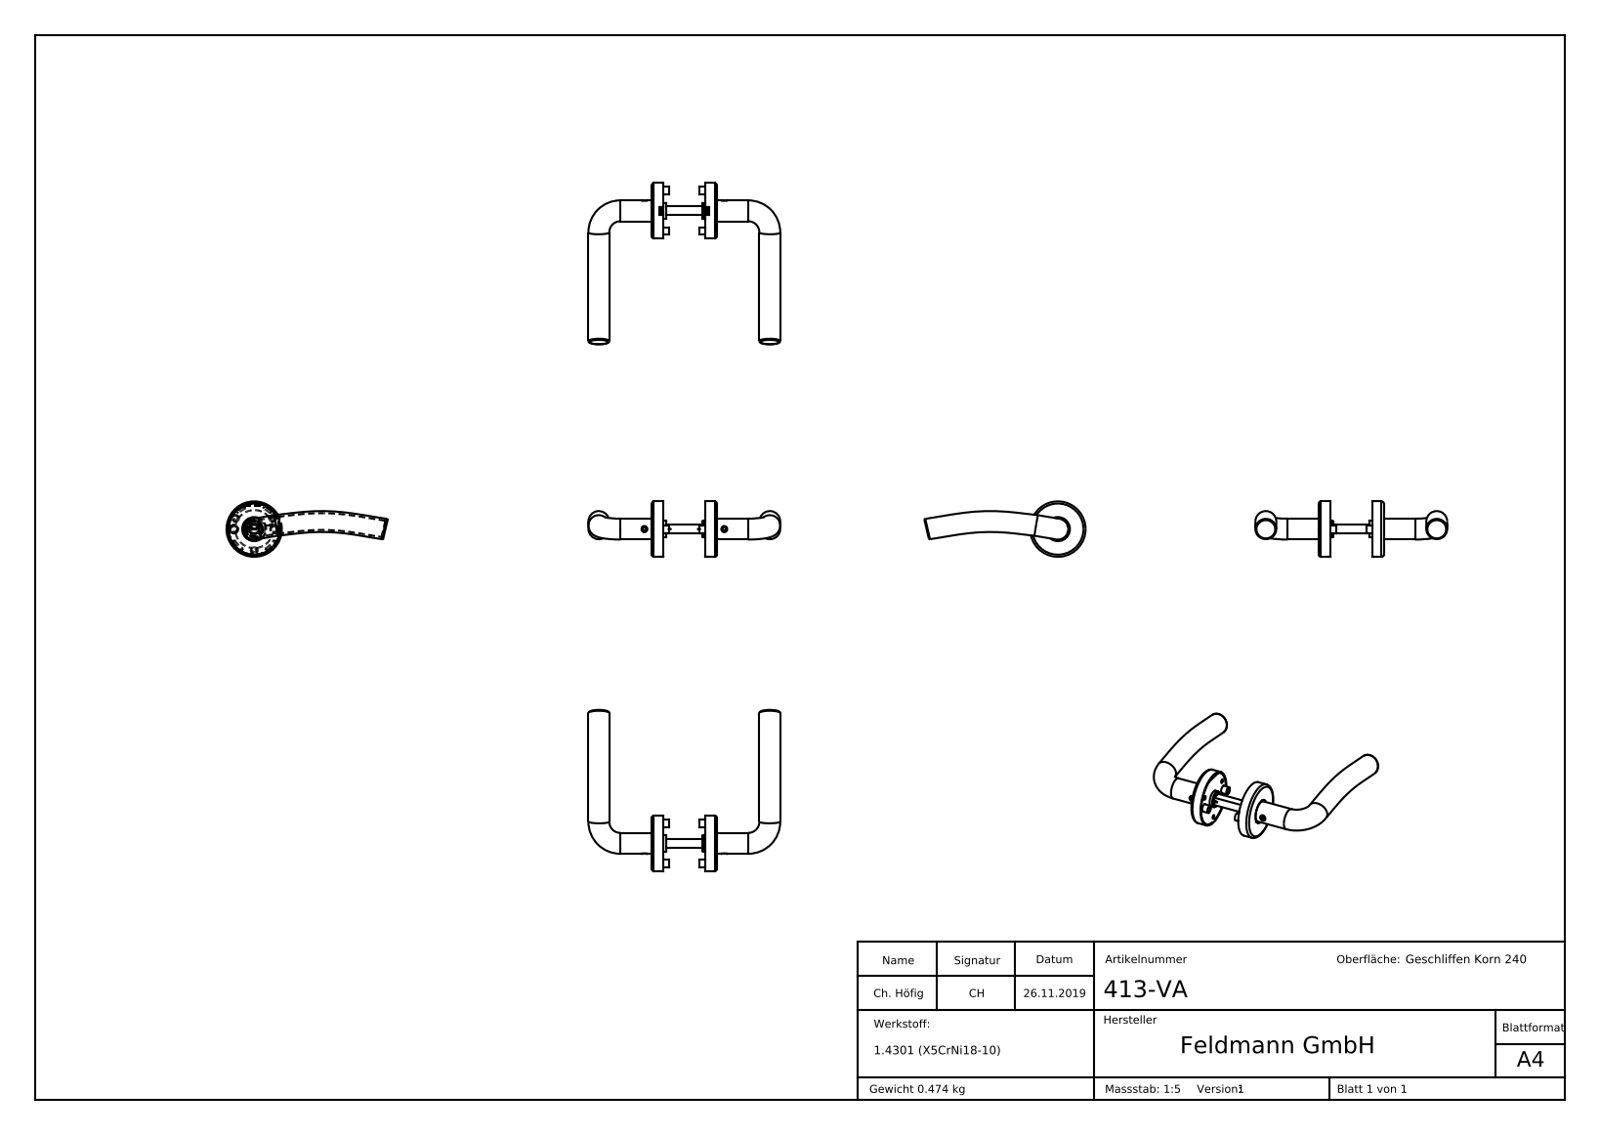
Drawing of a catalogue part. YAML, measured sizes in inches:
part_name: "4XX-VA Teil2_4XX-VA Teil2; 4XX-VA Teil3; 4XX-VA Teil2; 4XX-VA Teil1_413-VA Teil5 (+8 more)"
step_written_by: "SolidWorks 2015 (CONFIG_CONTROL_DESIGN)"
units: inches
bodies: {solids: 13, faces: 882, planar: 500, cylindrical: 118, other: 264}
overall_size: [2755.906, 236.215, 236.209]
volume: 6.534
surface_area: 151
round_holes:
  - {diameter: 0.146, count: 3}
  - {diameter: 0.197, count: 3}
  - {diameter: 0.24, count: 3}
  - {diameter: 0.217, count: 2}
  - {diameter: 0.287, count: 2}
  - {diameter: 0.315, count: 2}
  - {diameter: 0.606, count: 1}
  - {diameter: 0.618, count: 1}
  - {diameter: 0.638, count: 1}
  - {diameter: 0.89, count: 1}
round_bosses_or_shafts:
  - {diameter: 0.28, count: 2}
  - {diameter: 0.236, count: 2}
  - {diameter: 2.047, count: 1}
  - {diameter: 1.969, count: 1}
  - {diameter: 1.961, count: 1}
  - {diameter: 0.843, count: 1}
  - {diameter: 0.772, count: 1}
  - {diameter: 0.598, count: 1}
partial_cylinders:
  - {radius: 0.039, count: 4}
  - {radius: 0.177, count: 1}
  - {radius: 0.703, count: 1}
  - {radius: 0.827, count: 1}
  - {radius: 0.906, count: 1}
face_to_face_distances: [0.039, 2.362, 0.413, 1.988, 0.374, 1.949, 0.319, 1.575, 0.031, 0.315]
hole_center_spacings: [0.787, 1.364, 0.399, 0.748, 1.086, 1.483, 1.181, 1.496]
